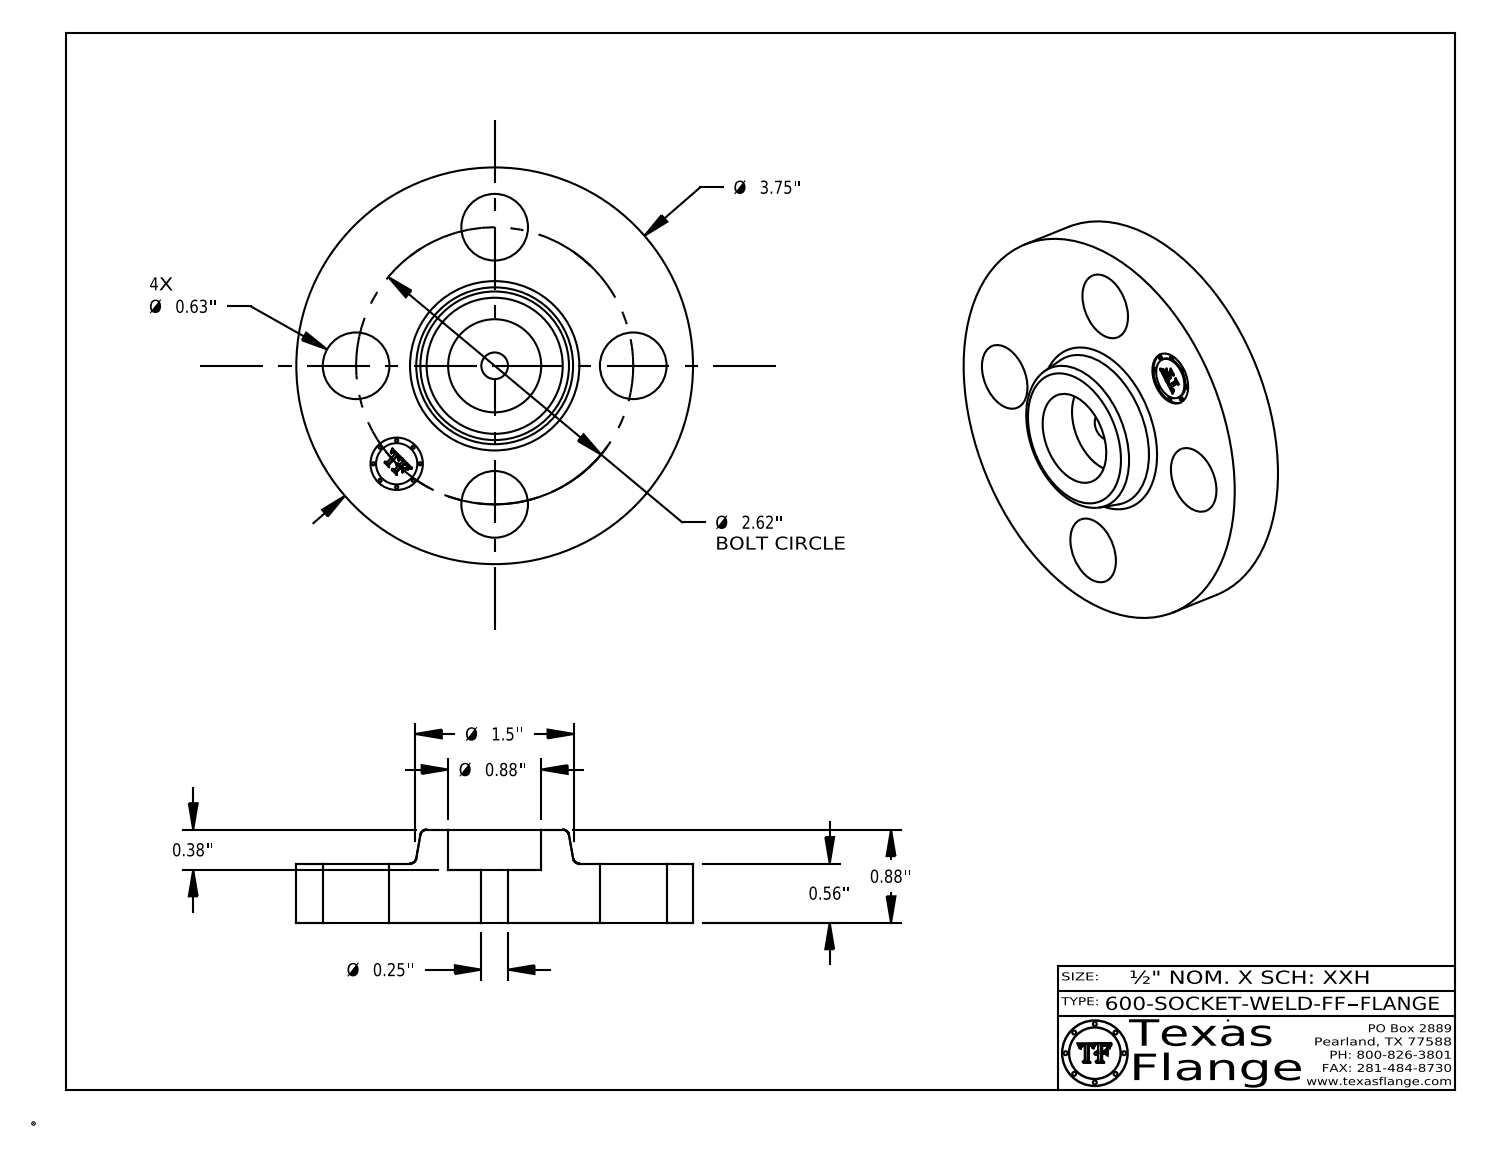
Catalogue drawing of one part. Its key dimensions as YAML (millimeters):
part_name: "600-SOCKET-WELD-FF"
step_written_by: "CATIA V5 STEP AP214 (AUTOMOTIVE_DESIGN)"
units: millimeters
bodies: {solids: 1, faces: 409, planar: 369, cylindrical: 34, other: 6}
overall_size: [95.3, 95.3, 22.4]
volume: 94290
surface_area: 21370
round_holes:
  - {diameter: 16, count: 4}
  - {diameter: 6.4, count: 1}
  - {diameter: 12.6, count: 1}
  - {diameter: 22.4, count: 1}
round_bosses_or_shafts:
  - {diameter: 0.8, count: 8}
  - {diameter: 95.3, count: 1}
  - {diameter: 9.9, count: 1}
face_to_face_distances: [14.2, 22.4, 8.1, 12.7, 1.5, 9.7, 13.8, 1.1, 0.4, 8.5]
hole_center_spacings: [33.3, 47, 25.5, 61.5, 66.5, 33.3]
